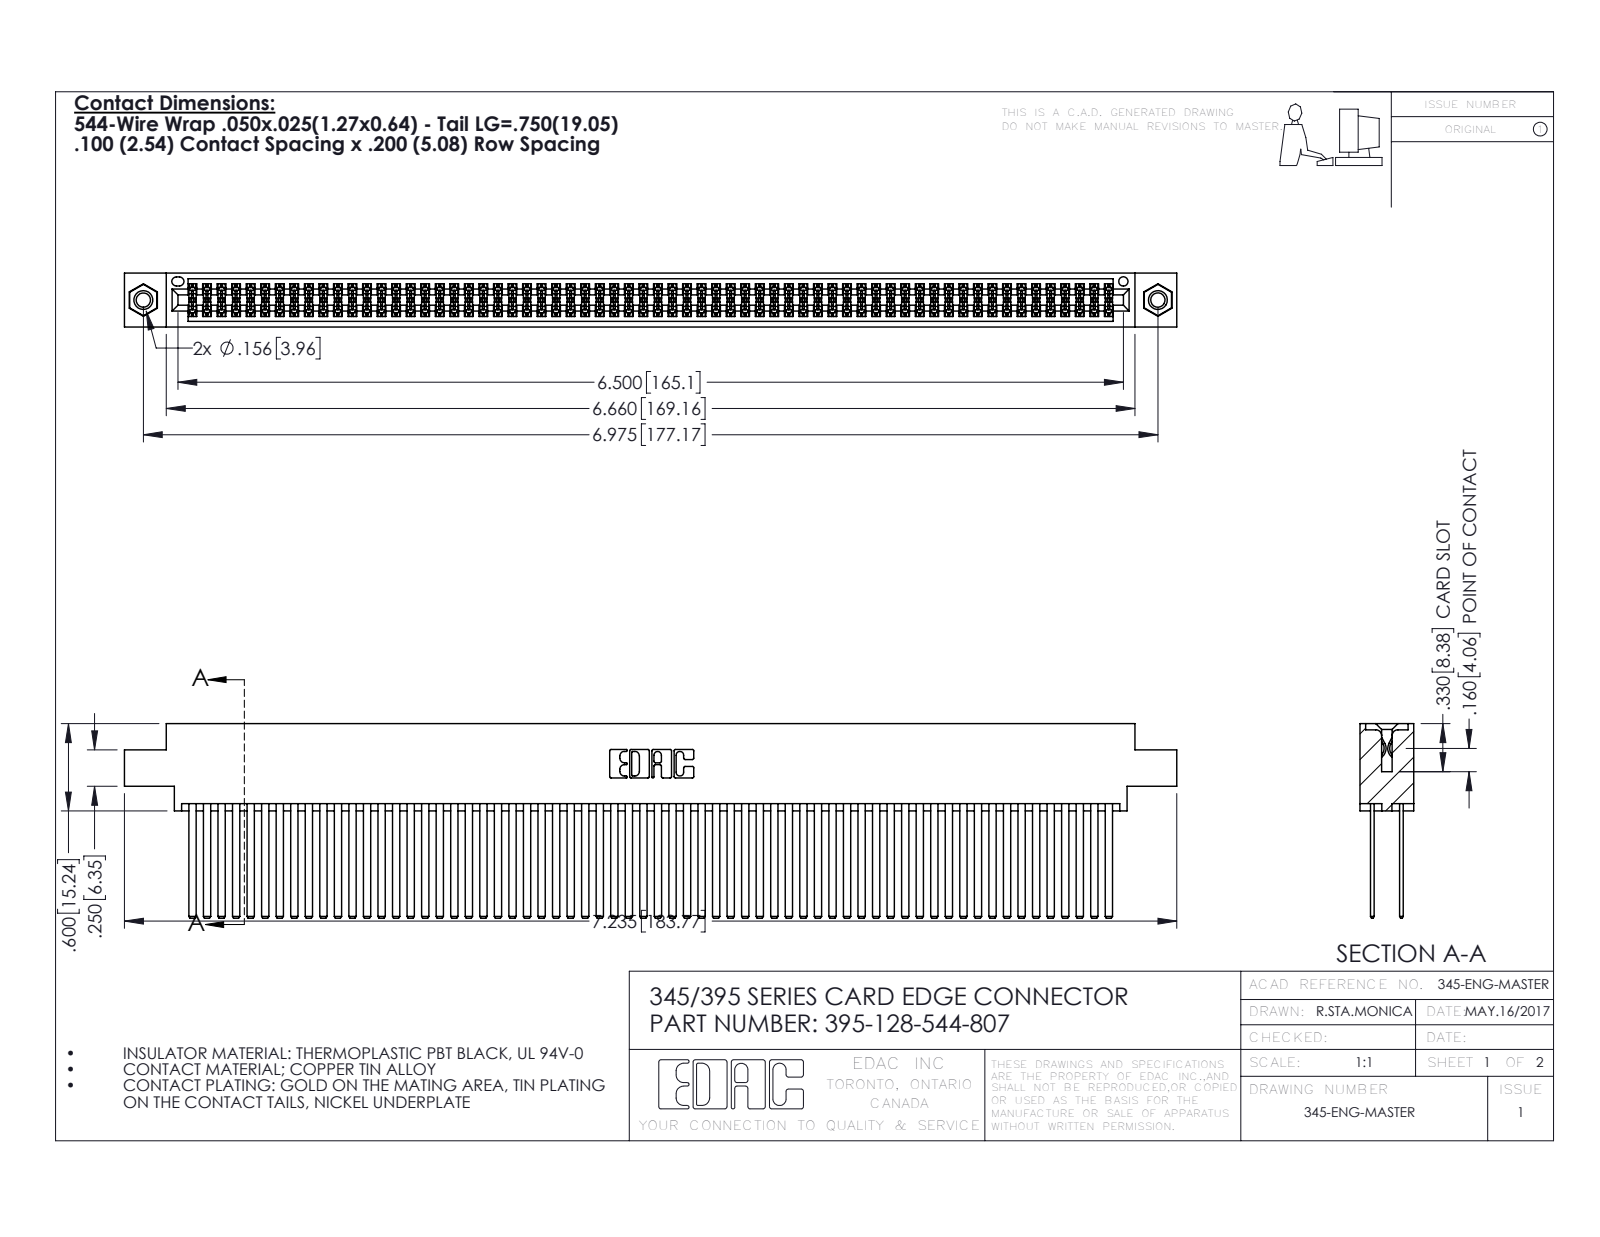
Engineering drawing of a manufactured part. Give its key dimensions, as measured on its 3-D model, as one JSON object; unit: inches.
{"part_name": "395-128-544-807; 345-250-001_345-250-005-103; 345 Part_0.170 Offset - 0.156 Dia-TI; 345-292-001_345-293-144", "step_written_by": "SolidWorks 2016 (CONFIG_CONTROL_DESIGN)", "units": "inches", "bodies": {"solids": 131, "faces": 5822, "planar": 3828, "cylindrical": 1978, "other": 16}, "overall_size": [7.235, 1.337, 0.37], "volume_in3": 1.204, "surface_area_in2": 54.27, "round_holes": [[0.098, 2], [0.125, 2], [0.156, 2], [0.064, 1]], "round_bosses_or_shafts": [[0.155, 2]], "partial_cylinders_radius": [[0.006, 192], [0.01, 22], [0.007, 6], [0.031, 6], [0.026, 3], [0.014, 2], [0.019, 2], [0.022, 2]], "face_to_face_distances": [0.2, 0.025, 0.072, 0.098, 0.272, 0.298, 0.225, 0.175, 0.37, 0.15], "hole_center_spacings": [0.27, 6.739, 6.975]}
